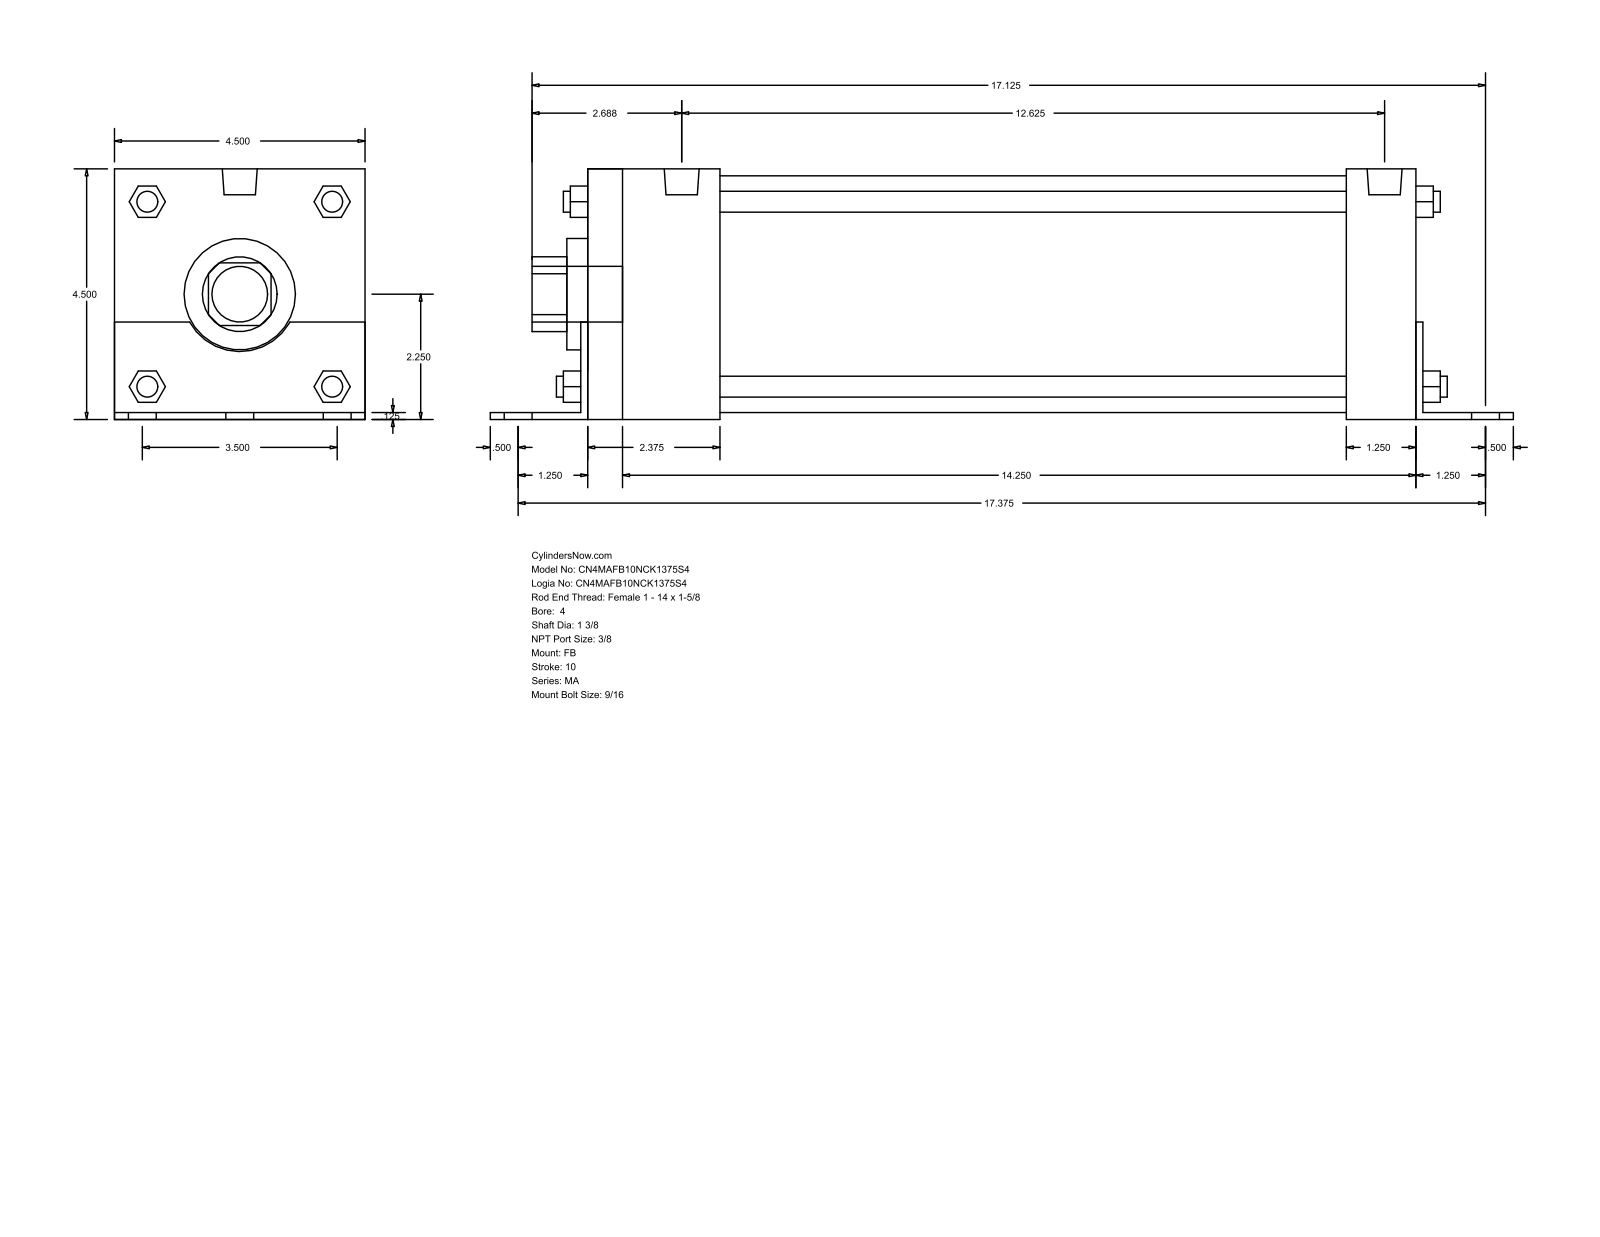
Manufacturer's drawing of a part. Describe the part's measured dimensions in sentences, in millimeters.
The part is named "MA_FB__0400_1.375". Its 3-D file was written by "GSSL Pune (CONFIG_CONTROL_DESIGN)". It is 0 solids with 140 faces: 105 planar, 35 cylindrical and 0 other. Overall it measures 466.73 by 114.35 by 114.3 millimeters. Round holes: 1 of diameter 34.92, 1 of diameter 50.8, 1 of diameter 107.95. Round bosses or shafts: 6 of diameter 14.29, 4 of diameter 11.11, 4 of diameter 9.53, 2 of diameter 15.93, 1 of diameter 25.4. Partial cylindrical surfaces (rounded edges, fillets, slot ends): 1 of radius 17.06, 1 of radius 26.16. The main face-to-face distances are 114.3, 3.17, 114.35, 3.12, 111.18, 381, 377.83, 60.32, 384.17, 31.75.
